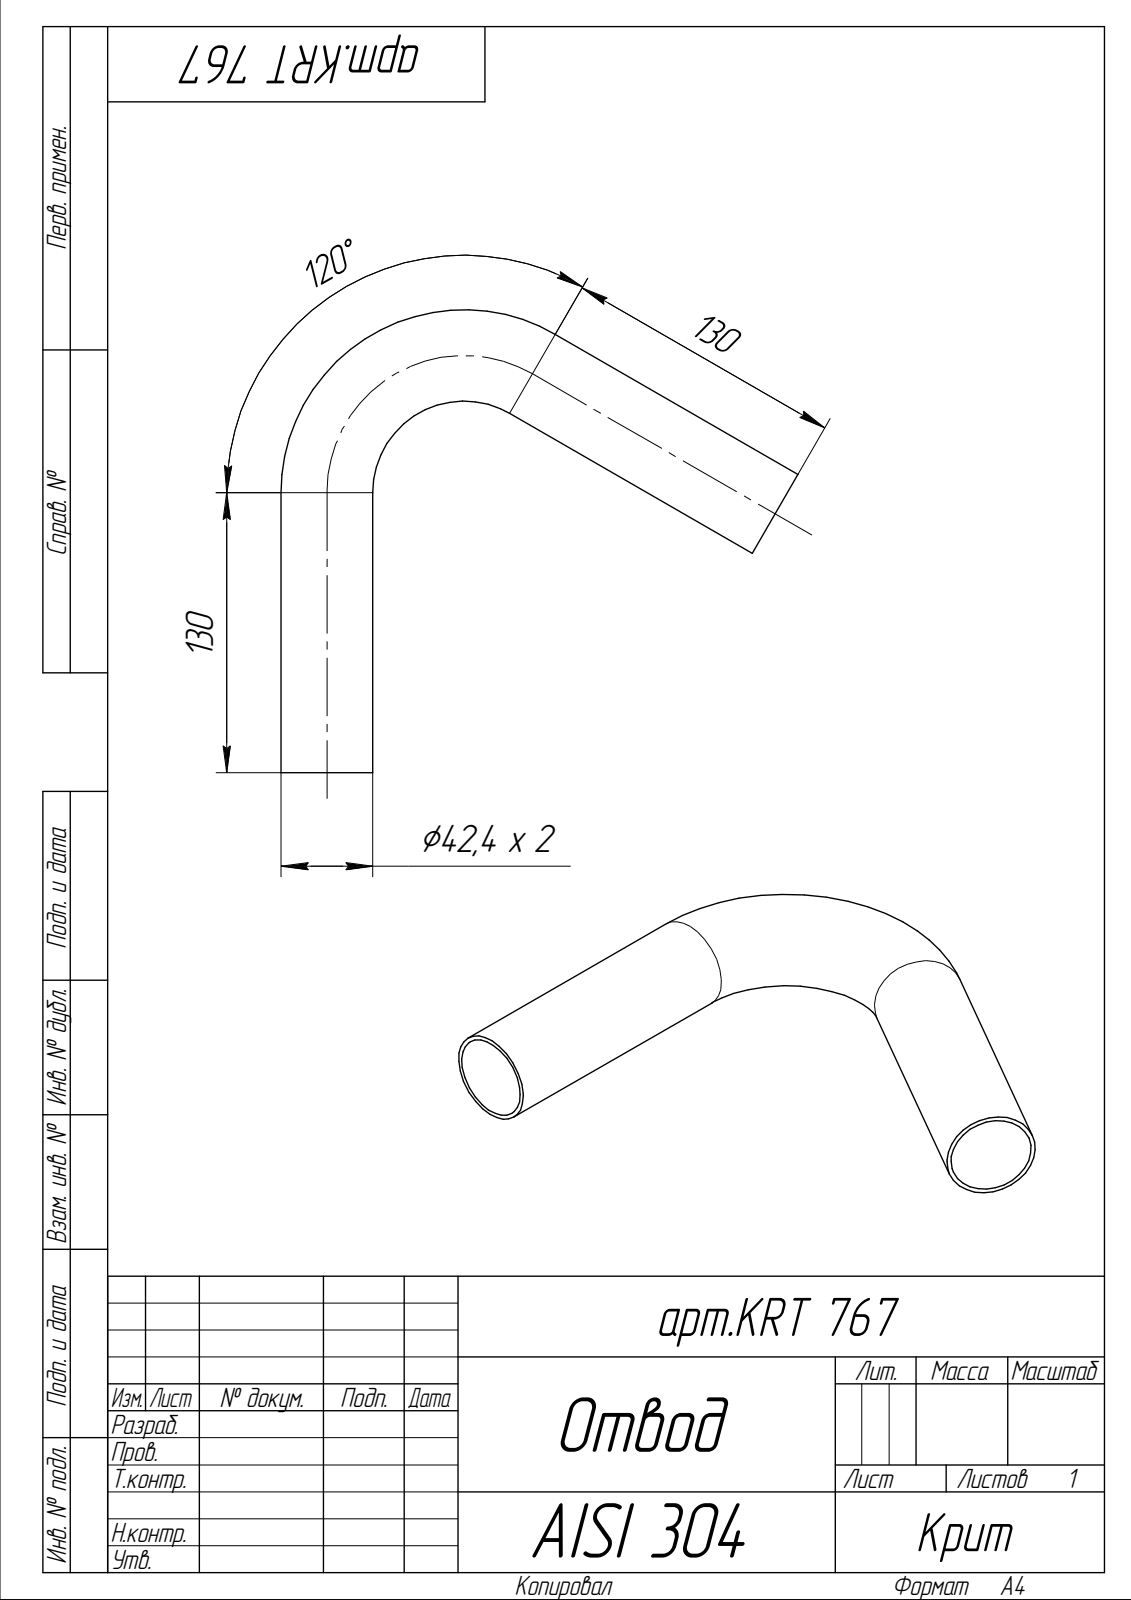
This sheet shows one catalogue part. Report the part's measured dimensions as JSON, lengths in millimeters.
{"part_name": "Деталь", "step_written_by": "ASCON Math Kernel (AUTOMOTIVE_DESIGN)", "units": "millimeters", "bodies": {"solids": 1, "faces": 8, "planar": 2, "cylindrical": 4, "other": 2}, "overall_size": [239.78, 214.8, 42.4], "volume_mm3": 99811, "surface_area_mm2": 100319, "round_holes": [[38.4, 2]], "round_bosses_or_shafts": [[42.4, 2]]}
